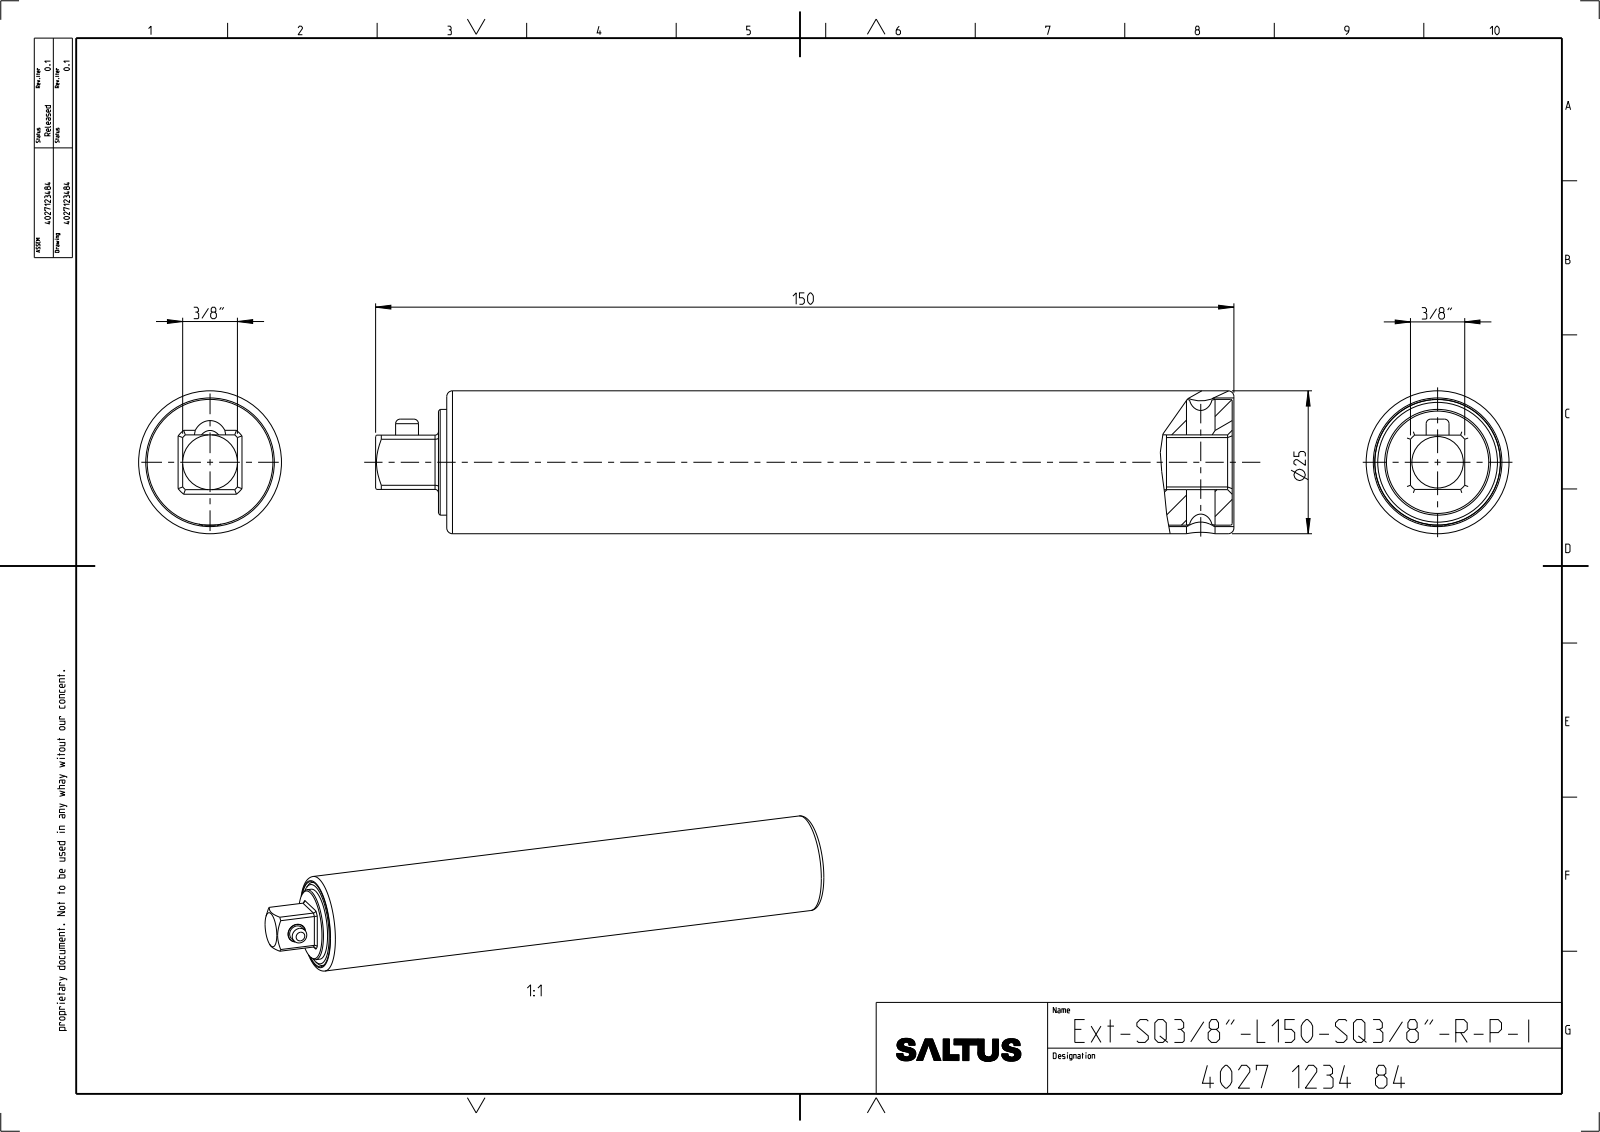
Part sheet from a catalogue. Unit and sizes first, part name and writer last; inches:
Units: inches
Overall size (bounding box): 5.913 × 0.984 × 0.984
Round holes (diameter × count): ⌀0.197 ×1, ⌀0.378 ×1
Round bosses / shafts (diameter × count): ⌀0.984 ×1, ⌀0.728 ×1, ⌀0.157 ×1
Partial cylindrical surfaces — rounded edges, fillets, slot ends (radius × count): R0.024 ×4, R0.118 ×1, R0.245 ×1
Main face-to-face distances: 0.376, 0.51, 4.959, 0.377, 0.374, 5.469, 0.057, 5.411, 4.902, 5.902
Bodies: 0 solids, 74 faces (26 planar, 23 cylindrical, 25 other)
Part name (STEP PRODUCT): 4027123484_ASM
STEP written by: CREO PARAMETRIC BY PTC INC, 2022414 (CONFIG_CONTROL_DESIGN)
